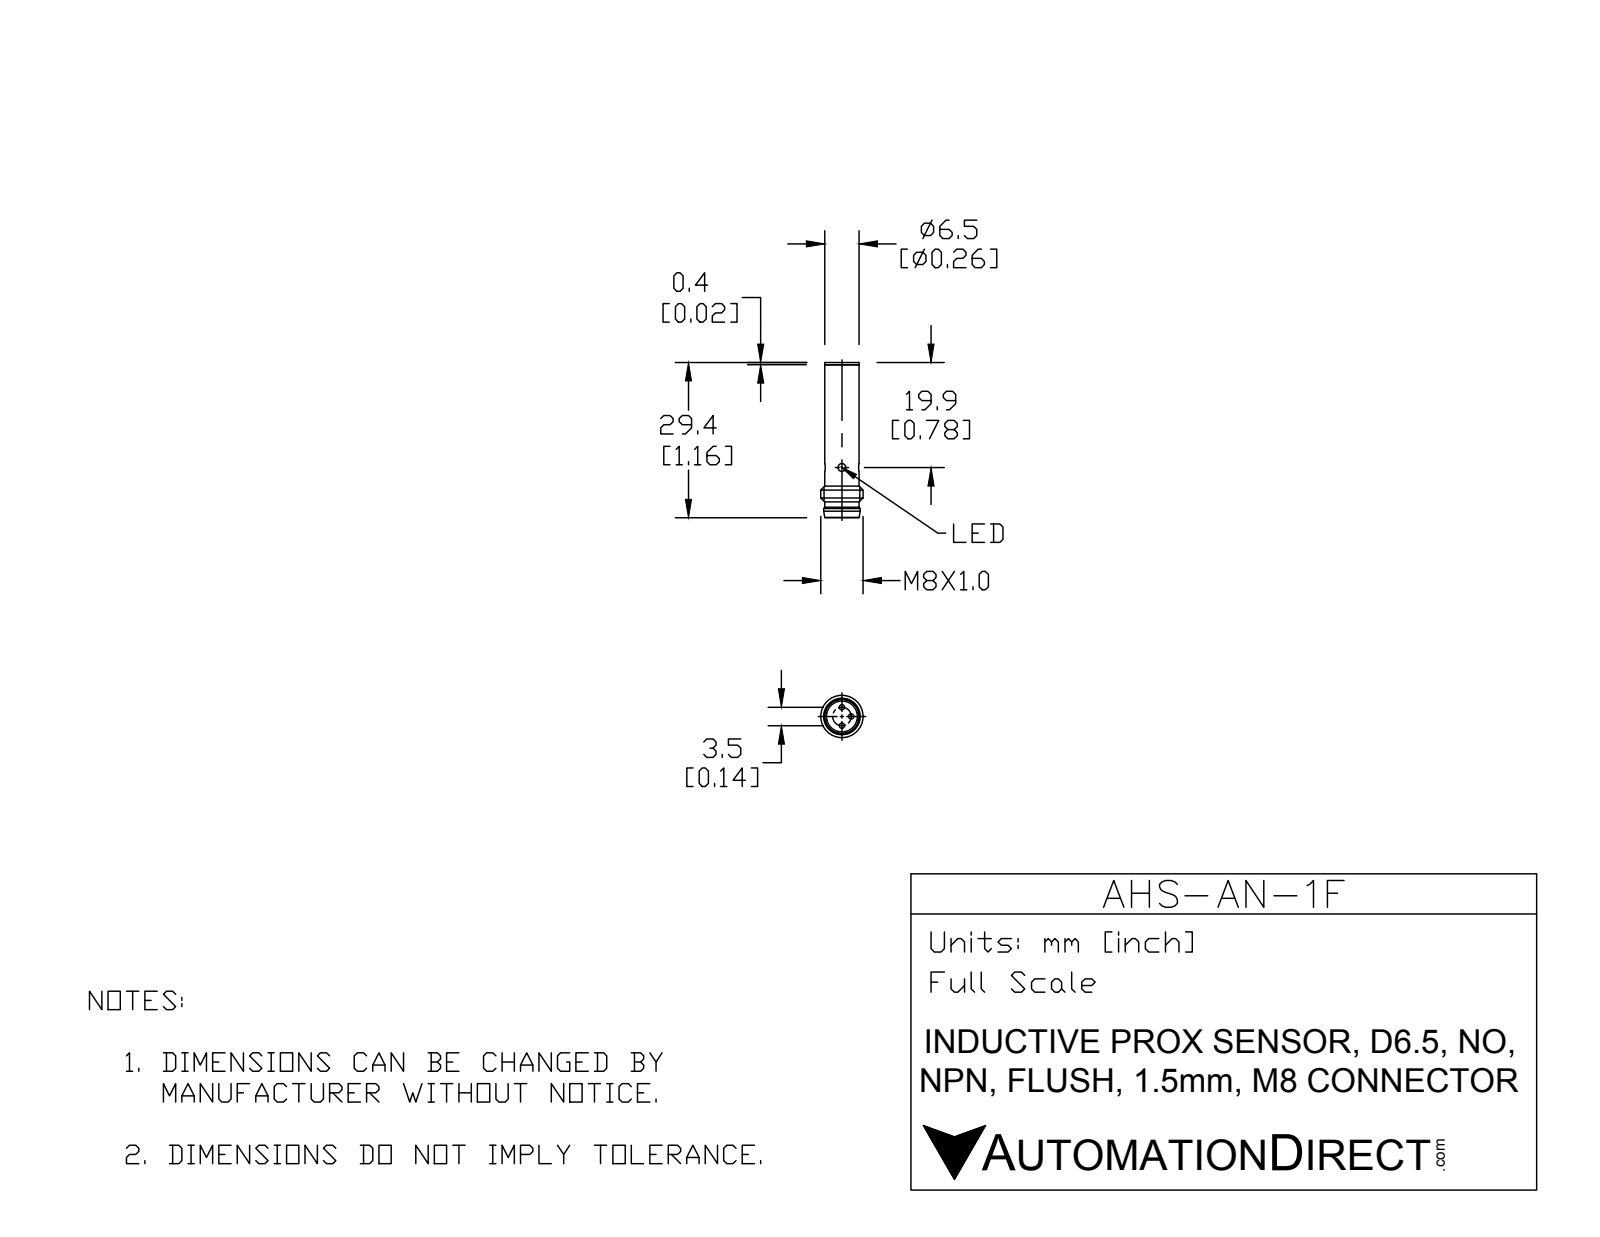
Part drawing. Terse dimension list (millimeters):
name: AHS-AN-1F
written by: SolidWorks 2015 (CONFIG_CONTROL_DESIGN)
unit: mm
bodies: 4 solids, 56 faces (12 planar, 26 cylindrical, 18 other)
size: 29.4 × 8 × 8
volume: 891 mm³; area: 842 mm²
holes: 2× ⌀1.5, 1× ⌀5.85
bosses: 3× ⌀1, 1× ⌀8, 1× ⌀6.9, 1× ⌀6.5
face distances: 24.4, 3, 27.4, 5.5, 2, 5, 29.4, 29, 27, 24
